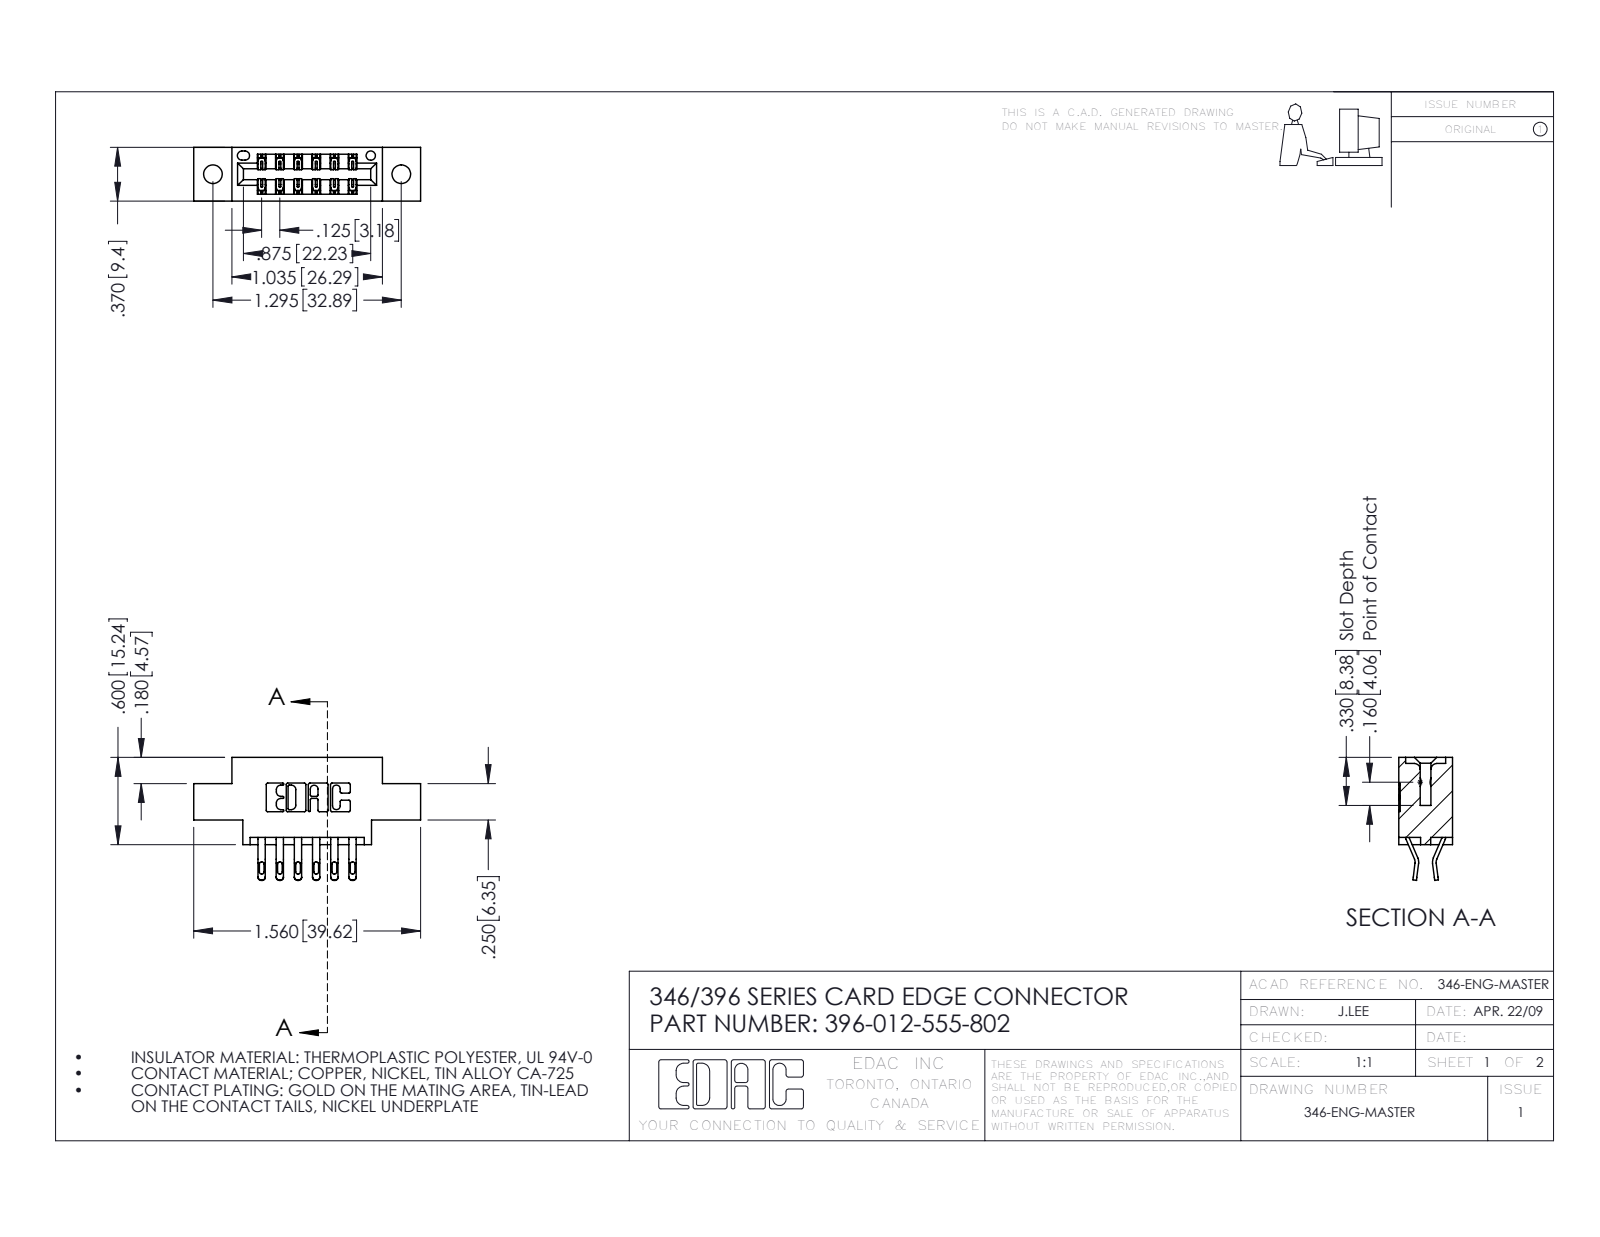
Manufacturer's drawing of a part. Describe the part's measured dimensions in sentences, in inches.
The part is named "396-012-555-802; 346 Part_0.170 Offset - 0.128 Dia; 345-292-001_555 Tail". Its 3-D file was written by "SolidWorks 2016 (CONFIG_CONTROL_DESIGN)". It is 13 solids with 822 faces: 476 planar, 346 cylindrical and 0 other. Overall it measures 1.56 by 0.845 by 0.37 inches. Its volume is 0.209 cubic inches and its surface area 6.479 square inches. Round holes: 2 of diameter 0.128, 1 of diameter 0.064. Partial cylindrical surfaces (rounded edges, fillets, slot ends): 24 of radius 0.016, 24 of radius 0.02, 22 of radius 0.01, 18 of radius 0.006, 6 of radius 0.007, 6 of radius 0.031, 3 of radius 0.026, 2 of radius 0.01. The main face-to-face distances are 0.25, 0.37, 0.048, 0.322, 0.148, 0.222, 0.1, 0.174, 0.025, 0.072. The hole center spacings are 0.246, 1.092, 1.295.
